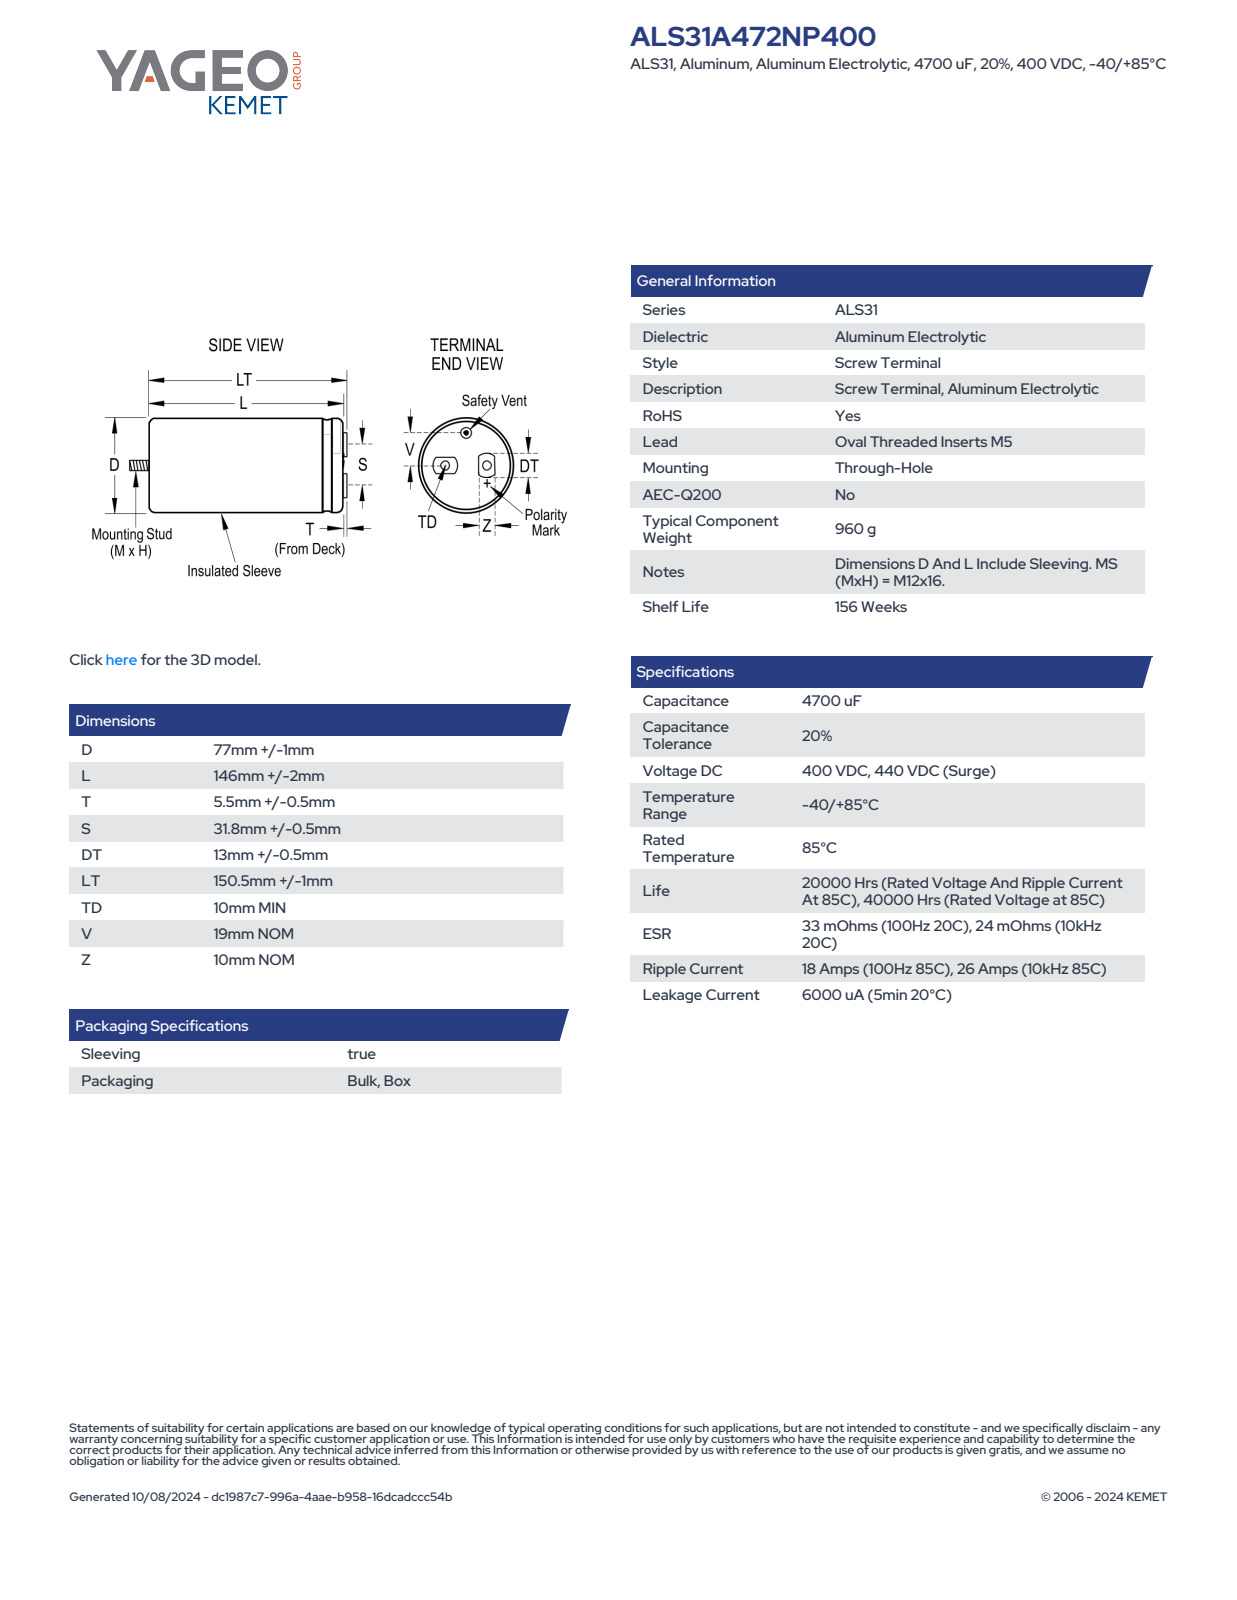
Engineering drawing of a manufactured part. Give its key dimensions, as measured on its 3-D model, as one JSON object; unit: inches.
{"part_name": "CARC_KALSOS_77X146_D78L148T6S31.8DT13.5TD10.000LT151.500V19.000", "step_written_by": "SolidWorks 2014 (AUTOMOTIVE_DESIGN)", "units": "inches", "bodies": {"solids": 1, "faces": 98, "planar": 35, "cylindrical": 24, "other": 39}, "overall_size": [6.594, 3.071, 3.071], "volume_in3": 42.93, "surface_area_in2": 73.54, "round_holes": [[0.197, 2], [0.079, 1], [2.913, 1]], "round_bosses_or_shafts": [[3.071, 1], [0.472, 1], [0.118, 1]], "partial_cylinders_radius": [[0.315, 4], [1.535, 1]], "face_to_face_distances": [5.787, 5.965, 0.177, 0.394, 0.63, 6.417, 6.594, 6.201, 5.571, 0.217], "hole_center_spacings": [0.626, 0.976, 0.748, 1.252]}
